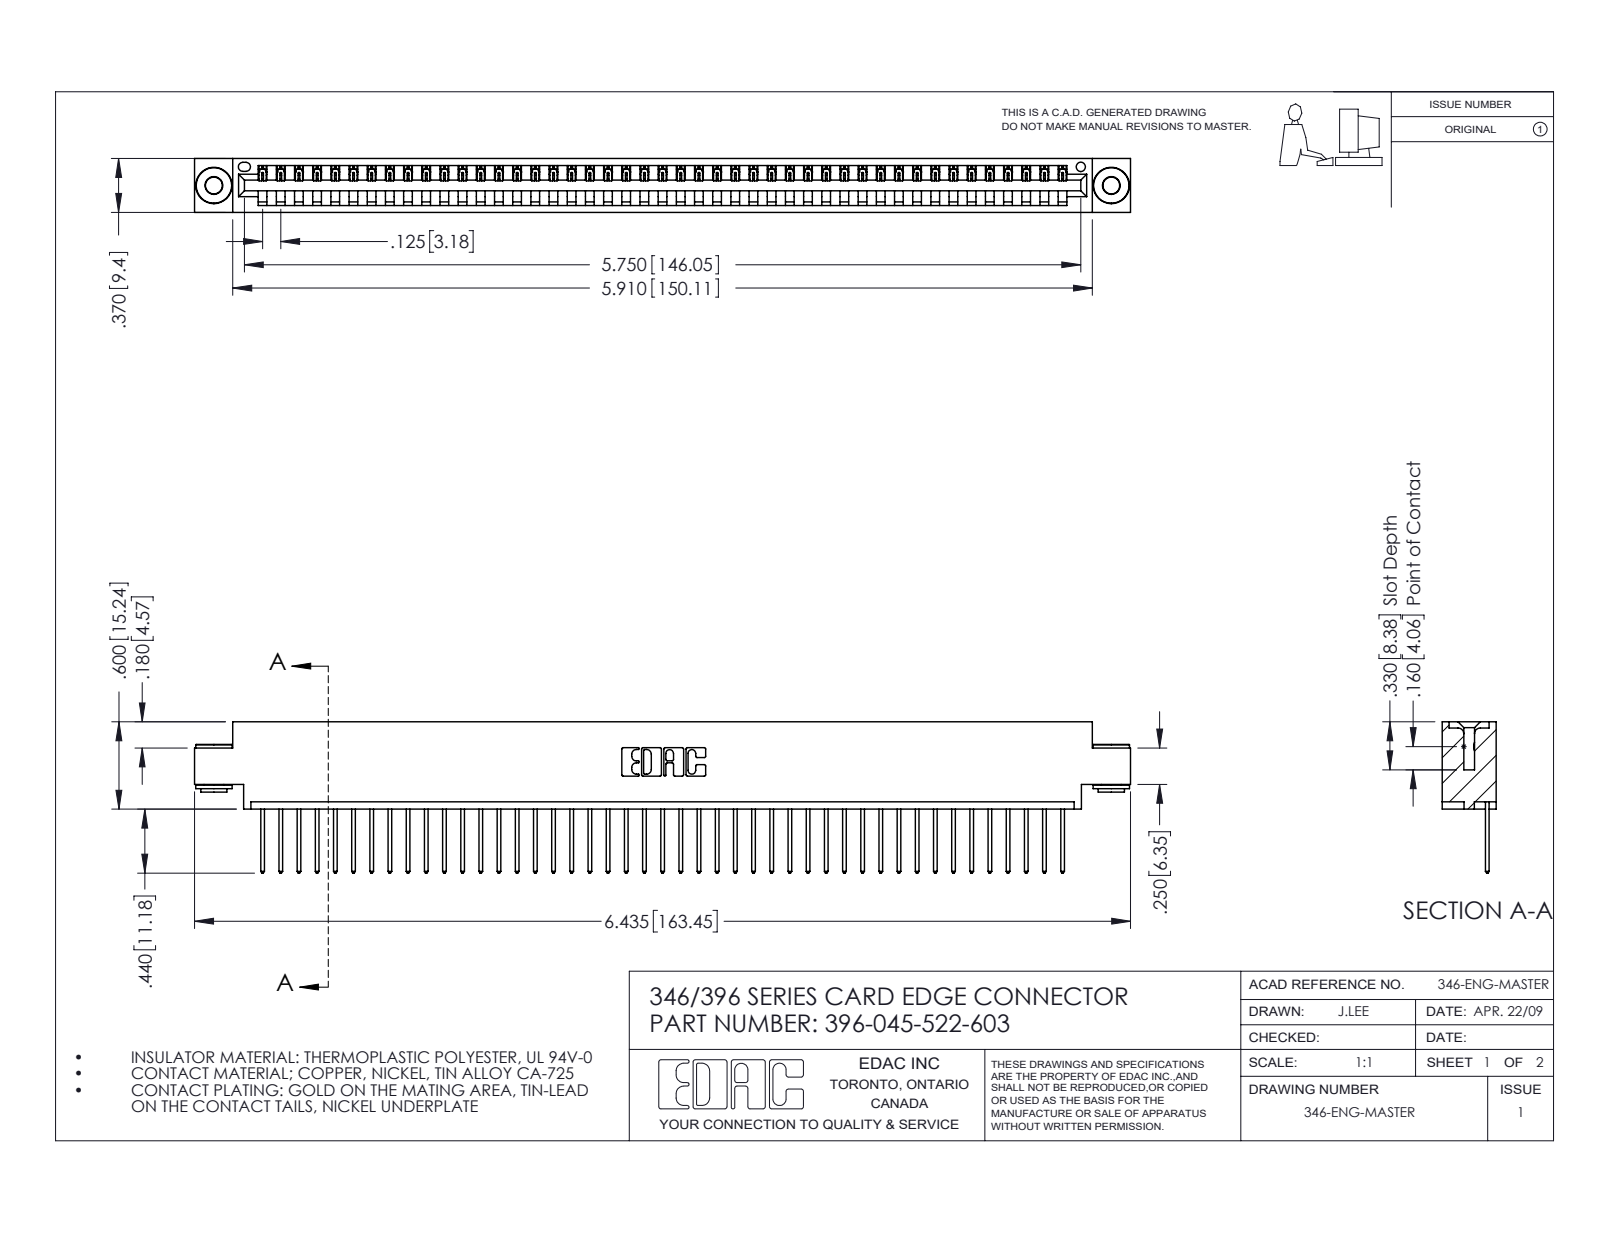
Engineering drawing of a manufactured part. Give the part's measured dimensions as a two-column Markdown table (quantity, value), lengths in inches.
| quantity | value |
| --- | --- |
| part name | 345-250-002_345-250-002-102; 345-292-001_345-293-122; 396-045-522-603; 346 Part_0.170 Offset - 0.156 Dia-TH |
| STEP written by | SolidWorks 2016 (CONFIG_CONTROL_DESIGN) |
| units | inches |
| bodies | 48 solids, 2774 faces (1890 planar, 876 cylindrical, 8 other) |
| overall size | 6.435 × 1.04 × 0.37 |
| volume | 0.948 in³ |
| surface area | 30.99 in² |
| round holes (diameter × count) | 0.116 × 2, 0.156 × 2, 0.064 × 1 |
| round bosses / shafts (diameter × count) | 0.25 × 2, 0.18 × 2, 0.136 × 2 |
| partial cylindrical surfaces (radius × count) | 0.006 × 90, 0.01 × 90, 0.01 × 22, 0.007 × 6, 0.031 × 6, 0.026 × 3, 0.031 × 2, 0.04 × 2 |
| main face-to-face distances | 0.048, 0.322, 0.37, 0.25, 0.025, 0.072, 0.298, 0.148, 0.222, 0.1 |
| hole center spacings | 0.246, 5.961, 6.17 |
